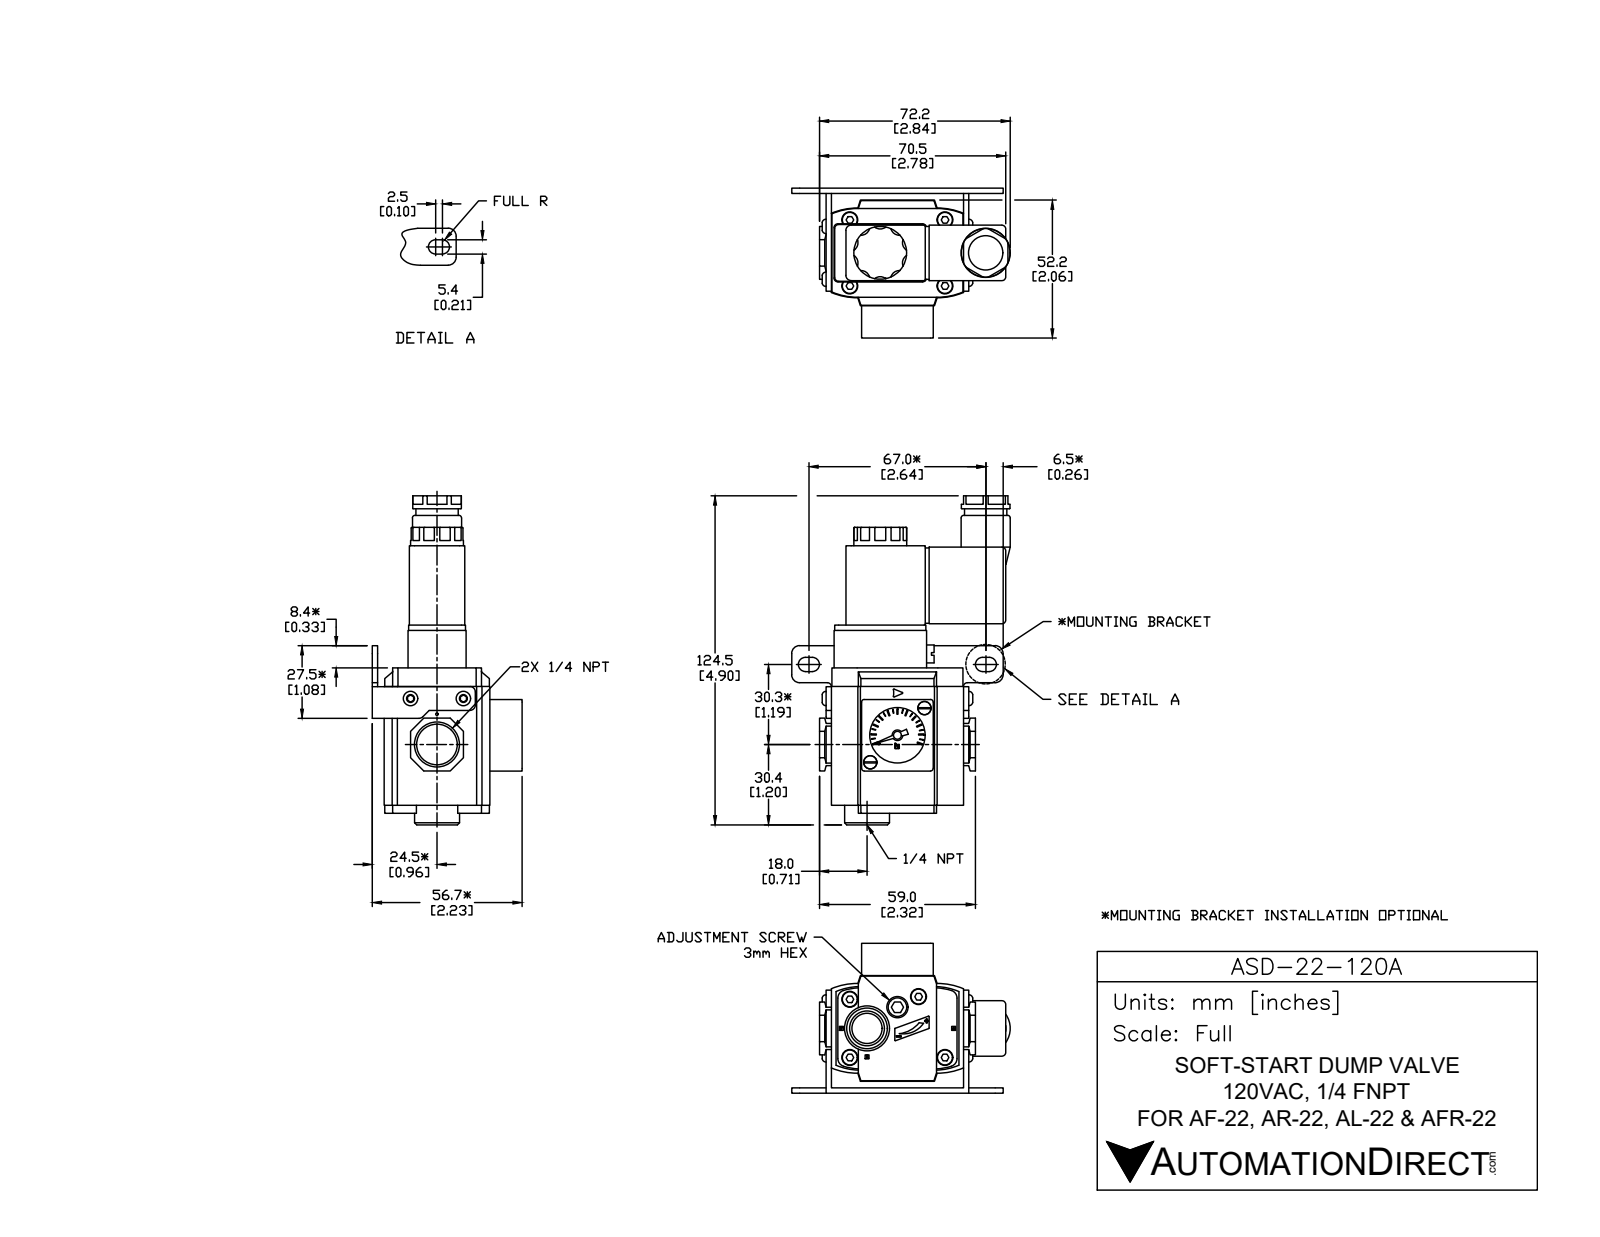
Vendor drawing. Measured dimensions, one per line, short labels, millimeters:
name: ASD-22-120A
written by: SolidWorks 2015 (CONFIG_CONTROL_DESIGN)
unit: mm
bodies: 22 solids, 568 faces (363 planar, 168 cylindrical, 37 other)
size: 124.5 × 82.7 × 56.7
volume: 163 664 mm³; area: 47 088 mm²
holes: 10× ⌀3, 8× ⌀6, 1× ⌀7, 1× ⌀8, 1× ⌀11.13, 1× ⌀11.45, 1× ⌀13, 1× ⌀17, 1× ⌀21
bosses: 4× ⌀5.6, 4× ⌀5.5, 2× ⌀2.5, 1× ⌀20, 1× ⌀18.6, 1× ⌀18.4, 1× ⌀16, 1× ⌀4
rounds: 10× R1.5, 10× R3.16, 6× R1, 6× R3, 4× R0.73, 4× R1.25, 4× R2.7, 4× R24.8
face distances: 52, 3, 2, 27.5, 6.5, 7, 45, 14, 5.5, 7.5
hole spacings: 1.5, 23.5, 36, 36.03, 42.99, 12.78, 14.09, 14.5
